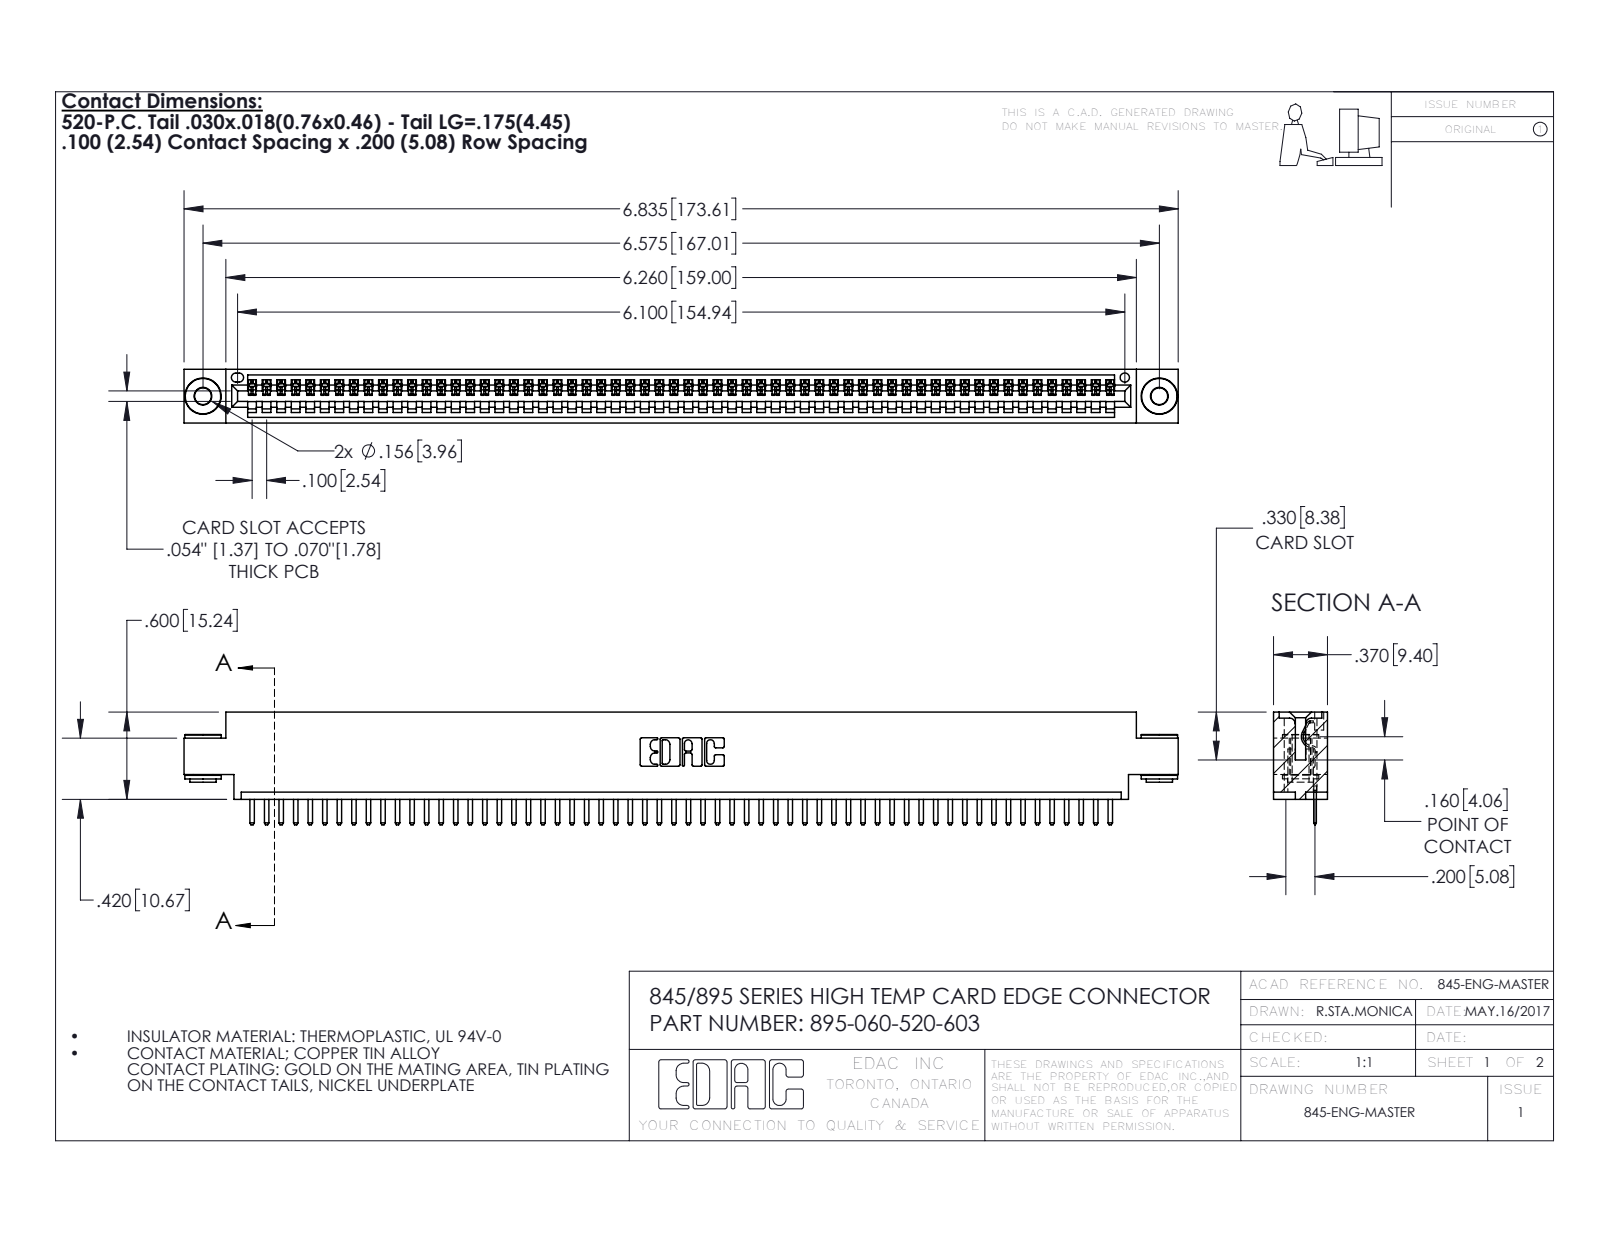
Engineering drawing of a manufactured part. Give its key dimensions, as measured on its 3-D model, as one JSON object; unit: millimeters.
{"part_name": "395-060-520-603; 345-250-002_345-250-002-102; 345-292-001_345-293-120; 345 Part_0.170 Offset - 0.156 Dia-TH", "step_written_by": "SolidWorks 2016 (CONFIG_CONTROL_DESIGN)", "units": "millimeters", "bodies": {"solids": 63, "faces": 3888, "planar": 2614, "cylindrical": 1266, "other": 8}, "overall_size": [173.6, 19.7, 9.4], "volume_mm3": 16400, "surface_area_mm2": 21770, "round_holes": [[2.9, 2], [4, 2], [1.6, 1]], "round_bosses_or_shafts": [[6.4, 2], [4.6, 2], [3.5, 2]], "partial_cylinders_radius": [[0.3, 122], [0.2, 120], [0.3, 22], [0.2, 6], [0.8, 6], [0.7, 3], [0.8, 2], [1, 2]], "face_to_face_distances": [1.8, 7.6, 9.4, 5.1, 2.5, 6.9, 0.6, 5.7, 1.8, 4.4], "hole_center_spacings": [6.9, 161, 167]}
